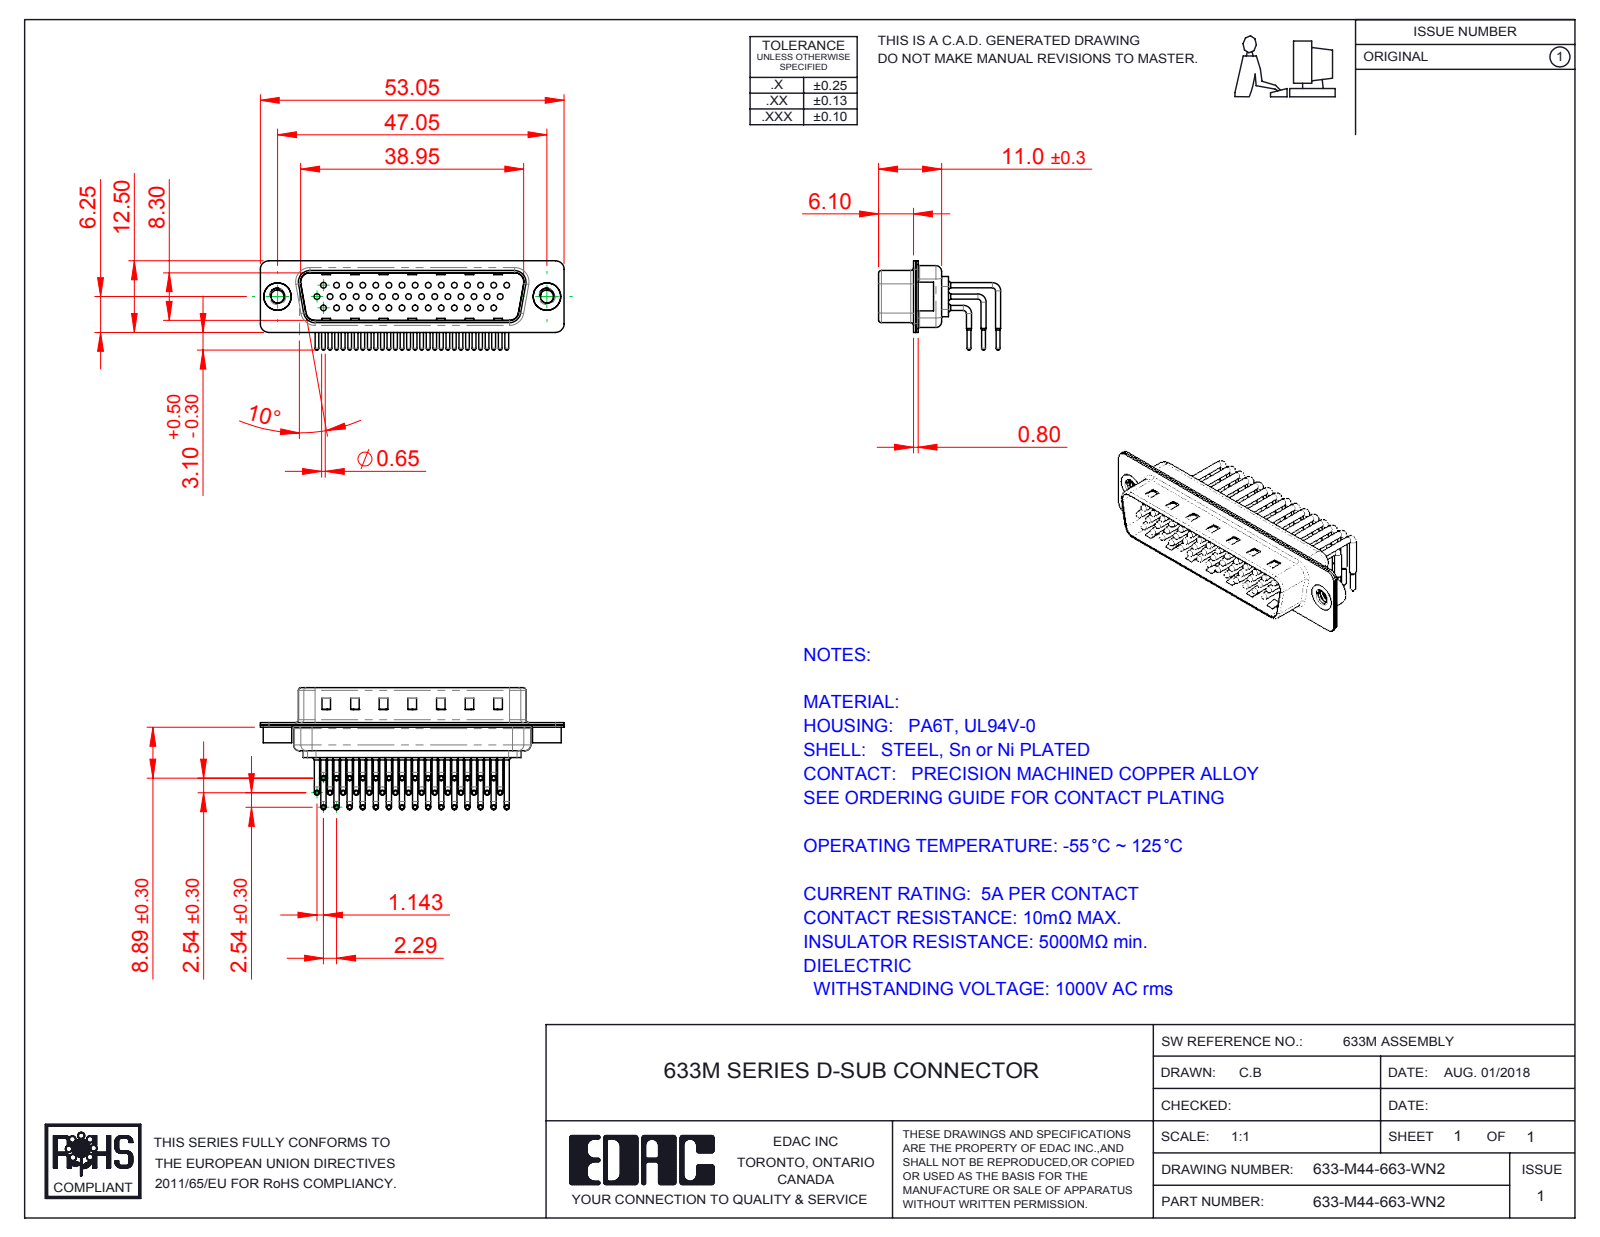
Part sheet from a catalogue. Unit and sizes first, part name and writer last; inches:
Units: inches
Overall size (bounding box): 2.089 × 0.839 × 0.614
Round holes (diameter × count): ⌀0.039 ×44, ⌀0.067 ×44, ⌀0.079 ×44, ⌀0.089 ×2, ⌀0.157 ×2, ⌀0.189 ×2
Round bosses / shafts (diameter × count): ⌀0.035 ×88, ⌀0.059 ×44, ⌀0.026 ×44, ⌀0.197 ×2, ⌀0.193 ×2, ⌀0.039 ×2
Partial cylindrical surfaces — rounded edges, fillets, slot ends (radius × count): R0.04 ×44, R0.059 ×16, R0.079 ×12, R0.02 ×8, R0.063 ×8, R0.01 ×4, R0.024 ×4, R0.026 ×4
Main face-to-face distances: 0.016, 0.033, 0.376, 0.059, 0.343, 0.075, 0.049, 0.409, 0.014, 0.36
Hole centre spacings: 0.09, 0.156, 0.09, 0.18, 0.324, 0.27, 0.45, 0.501
Volume: 0.191 in³ · Surface area: 15.59 in²
Bodies: 49 solids, 5216 faces (2987 planar, 1721 cylindrical, 508 other)
Part name (STEP PRODUCT): 633M Housing_44 Contacts; 633M Shell Front_44 Contacts; 633M Shell Rear_44 Contacts; 633M Contact Row 1 (+4 more)
STEP written by: SolidWorks 2016 (CONFIG_CONTROL_DESIGN)
